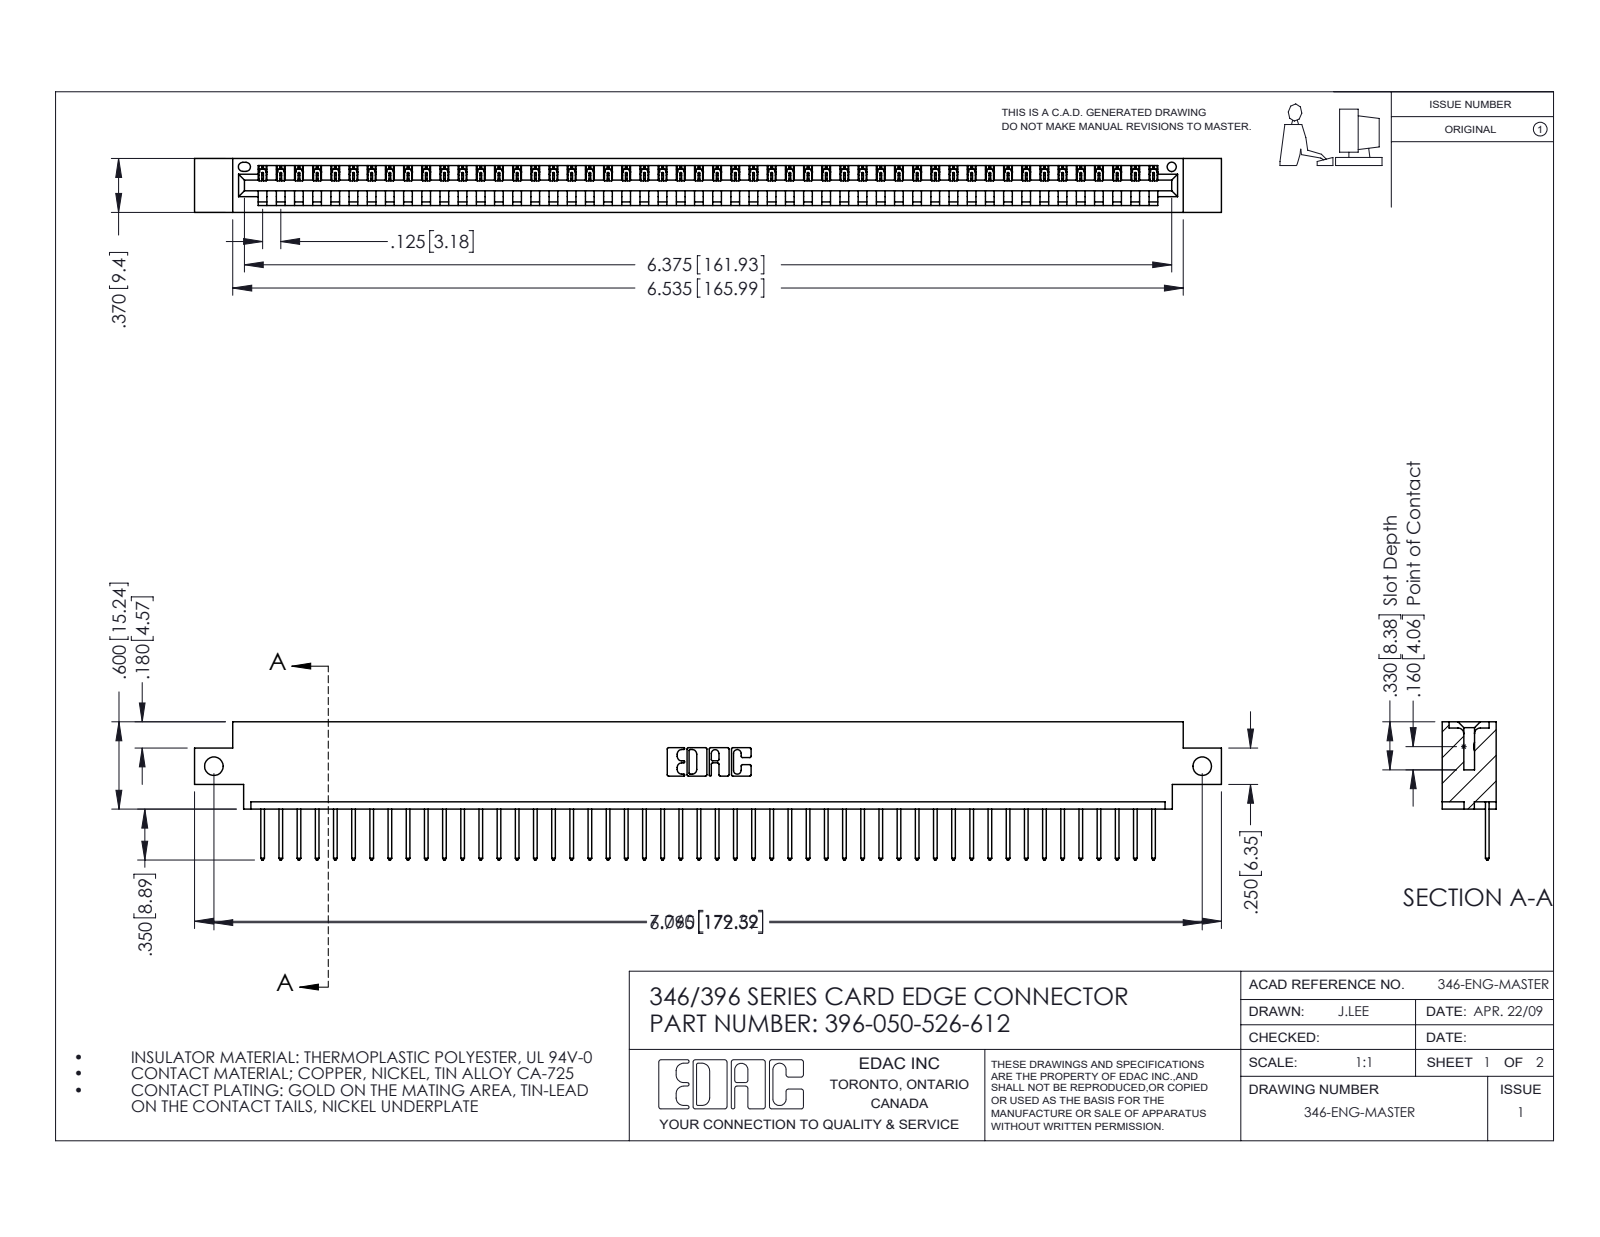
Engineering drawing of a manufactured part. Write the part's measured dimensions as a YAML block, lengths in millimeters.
part_name: "396-050-526-612; 346 Part_0.170 Offset - Side Mount; 345-292-001_345-293-126"
step_written_by: "SolidWorks 2016 (CONFIG_CONTROL_DESIGN)"
units: millimeters
bodies: {solids: 51, faces: 3026, planar: 2080, cylindrical: 946, other: 0}
overall_size: [179.3, 24.1, 9.4]
volume: 16940
surface_area: 21230
round_holes:
  - {diameter: 3.3, count: 2}
  - {diameter: 1.6, count: 1}
partial_cylinders:
  - {radius: 0.2, count: 100}
  - {radius: 0.3, count: 100}
  - {radius: 0.3, count: 22}
  - {radius: 0.2, count: 6}
  - {radius: 0.8, count: 6}
  - {radius: 0.7, count: 3}
  - {radius: 0.8, count: 2}
  - {radius: 1, count: 2}
face_to_face_distances: [1.2, 8.2, 9.4, 6.4, 1.8, 7.6, 0.6, 3.8, 5.6, 2.5]
hole_center_spacings: [172.6]
